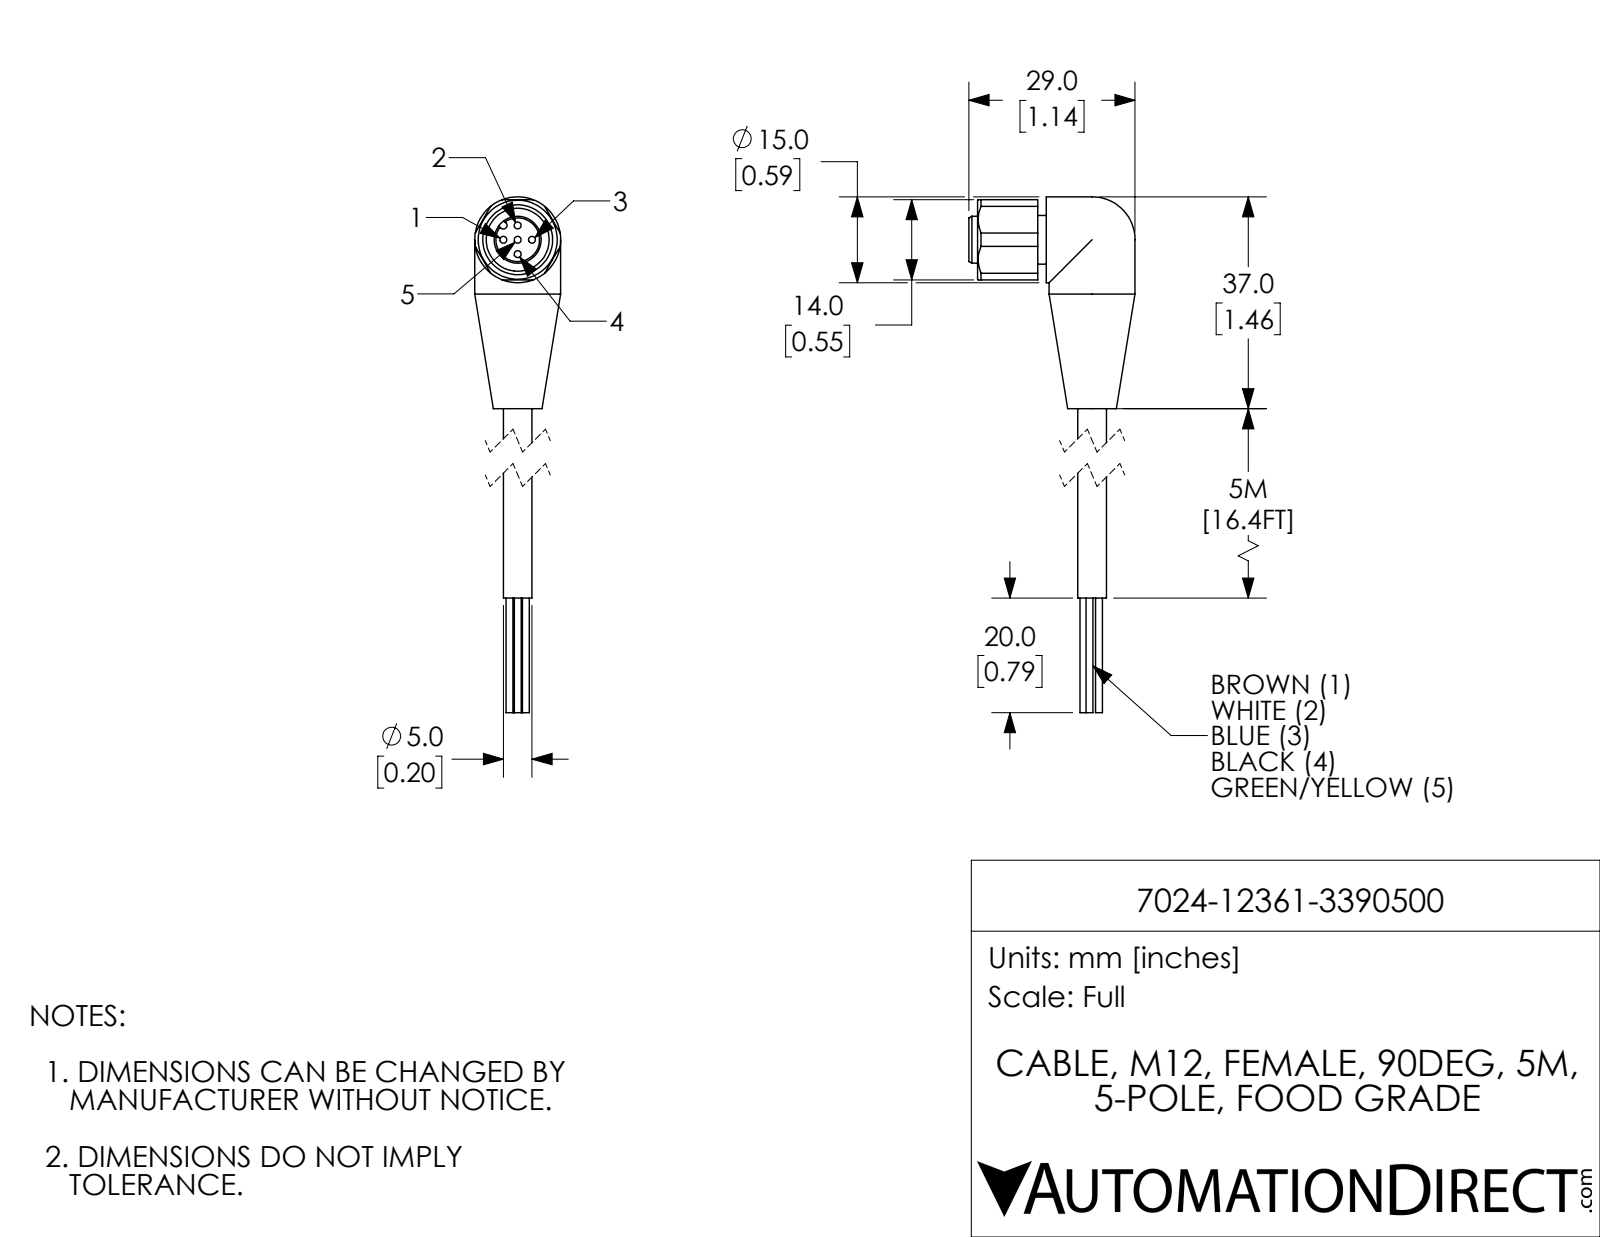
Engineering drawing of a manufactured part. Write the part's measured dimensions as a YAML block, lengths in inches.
part_name: "7024-12361-3390500"
step_written_by: "SolidWorks 2018 (AUTOMOTIVE_DESIGN)"
units: inches
bodies: {solids: 1, faces: 76, planar: 26, cylindrical: 40, other: 10}
overall_size: [3.425, 1.142, 0.591]
volume: 0.453
surface_area: 6.14
round_holes:
  - {diameter: 0.047, count: 5}
  - {diameter: 0.433, count: 1}
round_bosses_or_shafts:
  - {diameter: 0.047, count: 5}
  - {diameter: 0.591, count: 2}
  - {diameter: 0.335, count: 1}
  - {diameter: 0.323, count: 1}
  - {diameter: 0.197, count: 1}
partial_cylinders:
  - {radius: 0.026, count: 1}
face_to_face_distances: [0.551, 0.059, 0.472, 0.177, 0.118, 0.531, 0.354, 0.886, 1.437, 0.413]
hole_center_spacings: [0.098, 0.139, 0.197]
